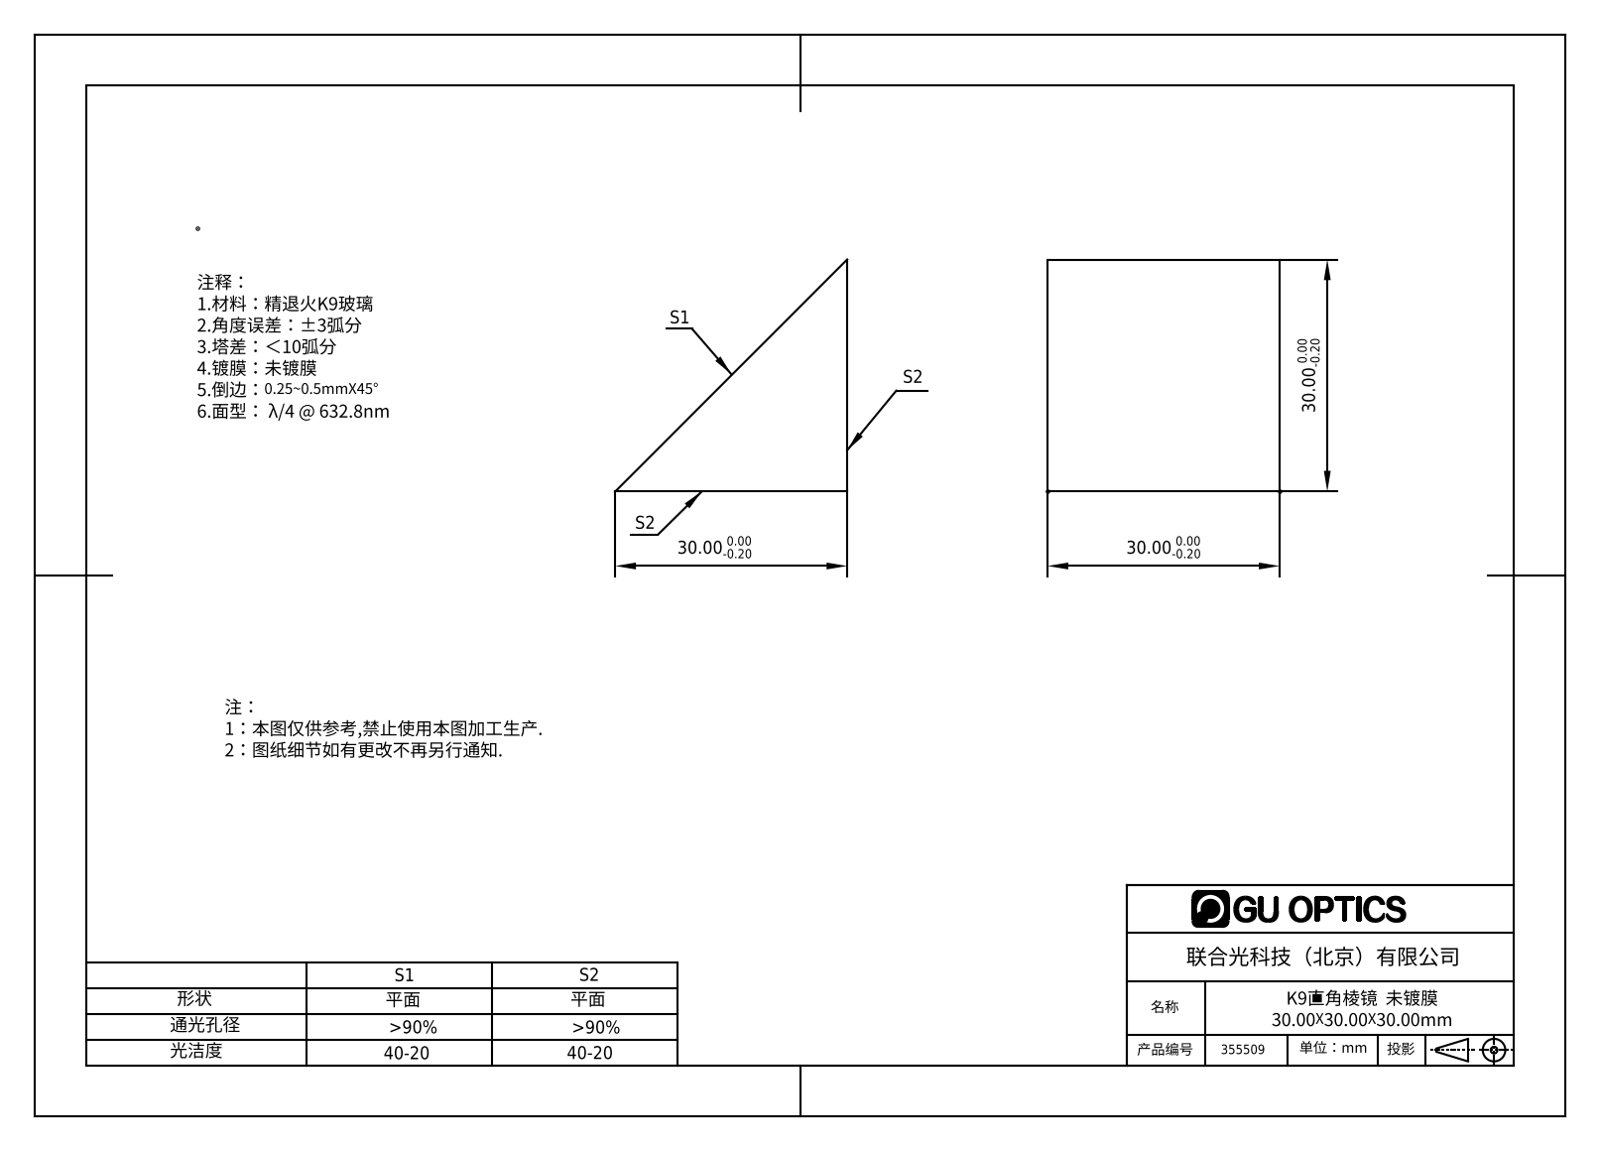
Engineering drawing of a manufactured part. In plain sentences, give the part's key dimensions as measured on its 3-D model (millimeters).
The part is named "355509". Its 3-D file was written by "SolidWorks 2016 (CONFIG_CONTROL_DESIGN)". It is 1 solid with 5 faces: 5 planar, 0 cylindrical and 0 other. Overall it measures 30 by 30 by 30 millimeters. Its volume is 13 500 cubic millimeters and its surface area 3 973 square millimeters. The main face-to-face distances are 30.
